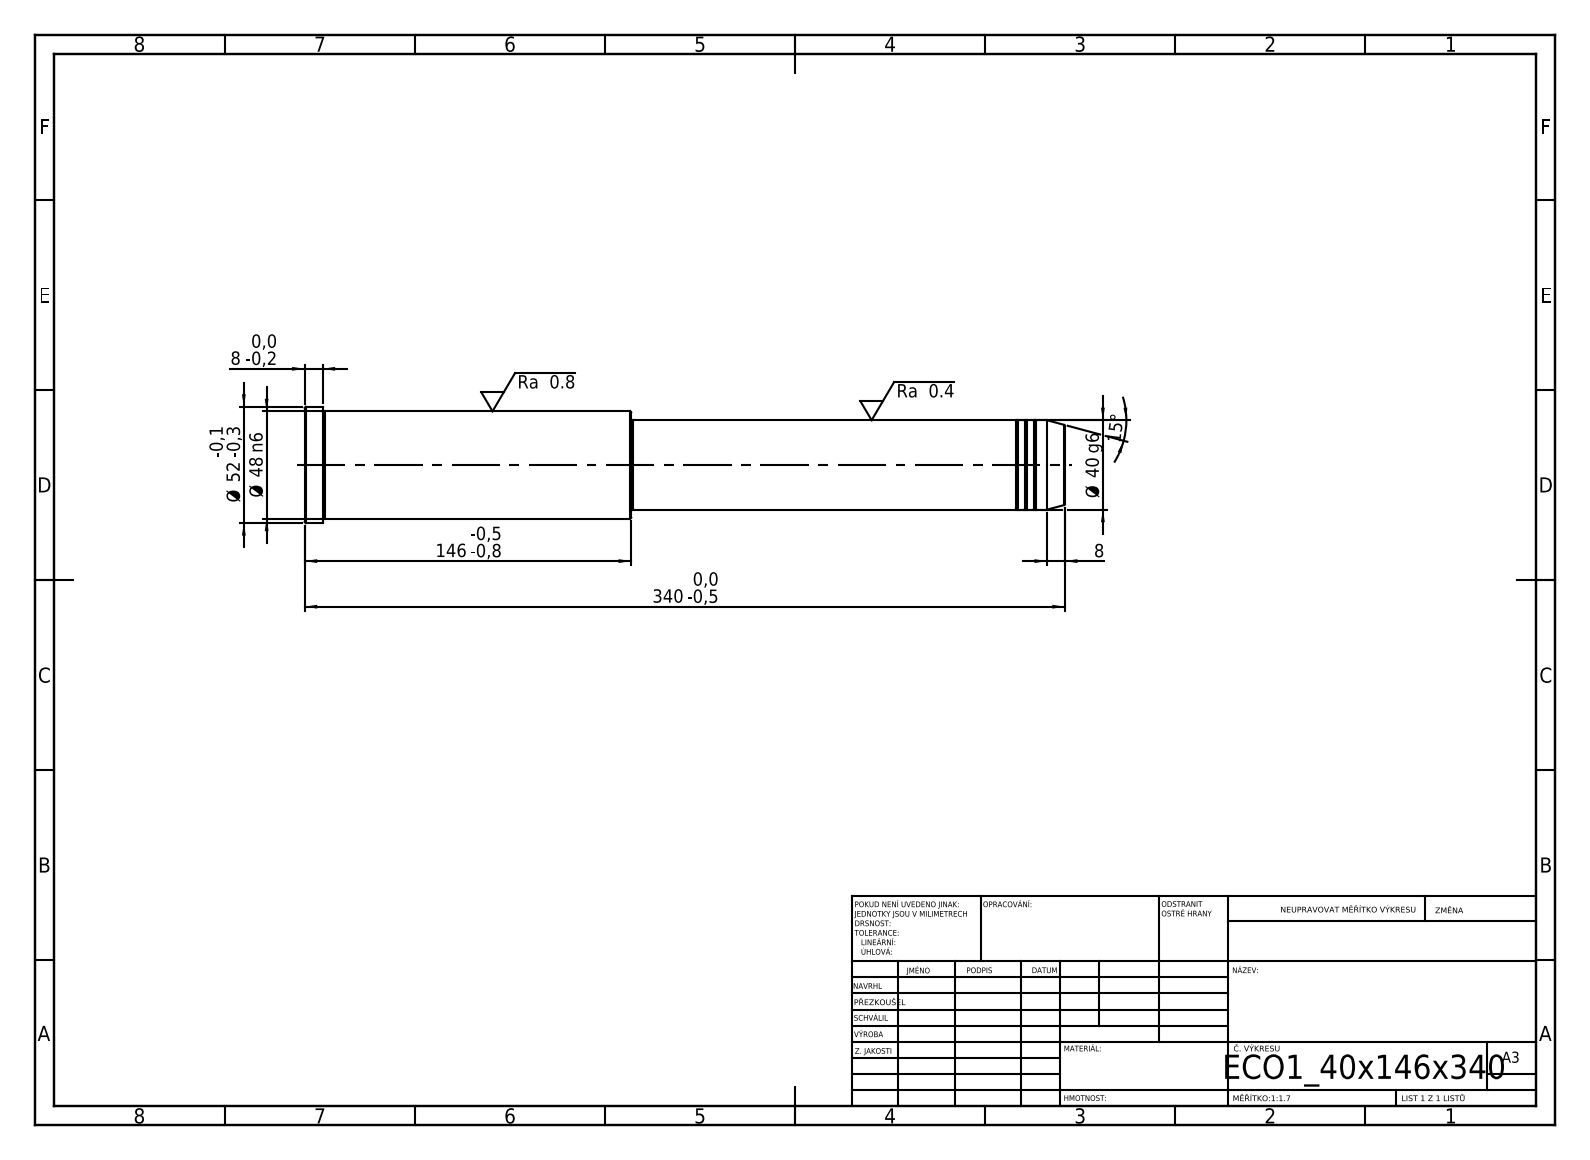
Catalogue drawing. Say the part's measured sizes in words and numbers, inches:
Its 3-D file was written by "SolidWorks 2019 (CONFIG_CONTROL_DESIGN)". It is 1 solid with 43 faces: 5 planar, 14 cylindrical and 24 other. Overall it measures 13.386 by 2.047 by 2.047 inches. Its volume is 31.07 cubic inches and its surface area 78.7 square inches. Round bosses or shafts: 1 of diameter 2.047, 1 of diameter 1.89, 1 of diameter 1.575, 1 of diameter 1.535. The main face-to-face distances are 13.386, 7.638, 5.748, 13.071, 5.433, 0.315, 7.598, 0.039, 5.472, 5.787.
